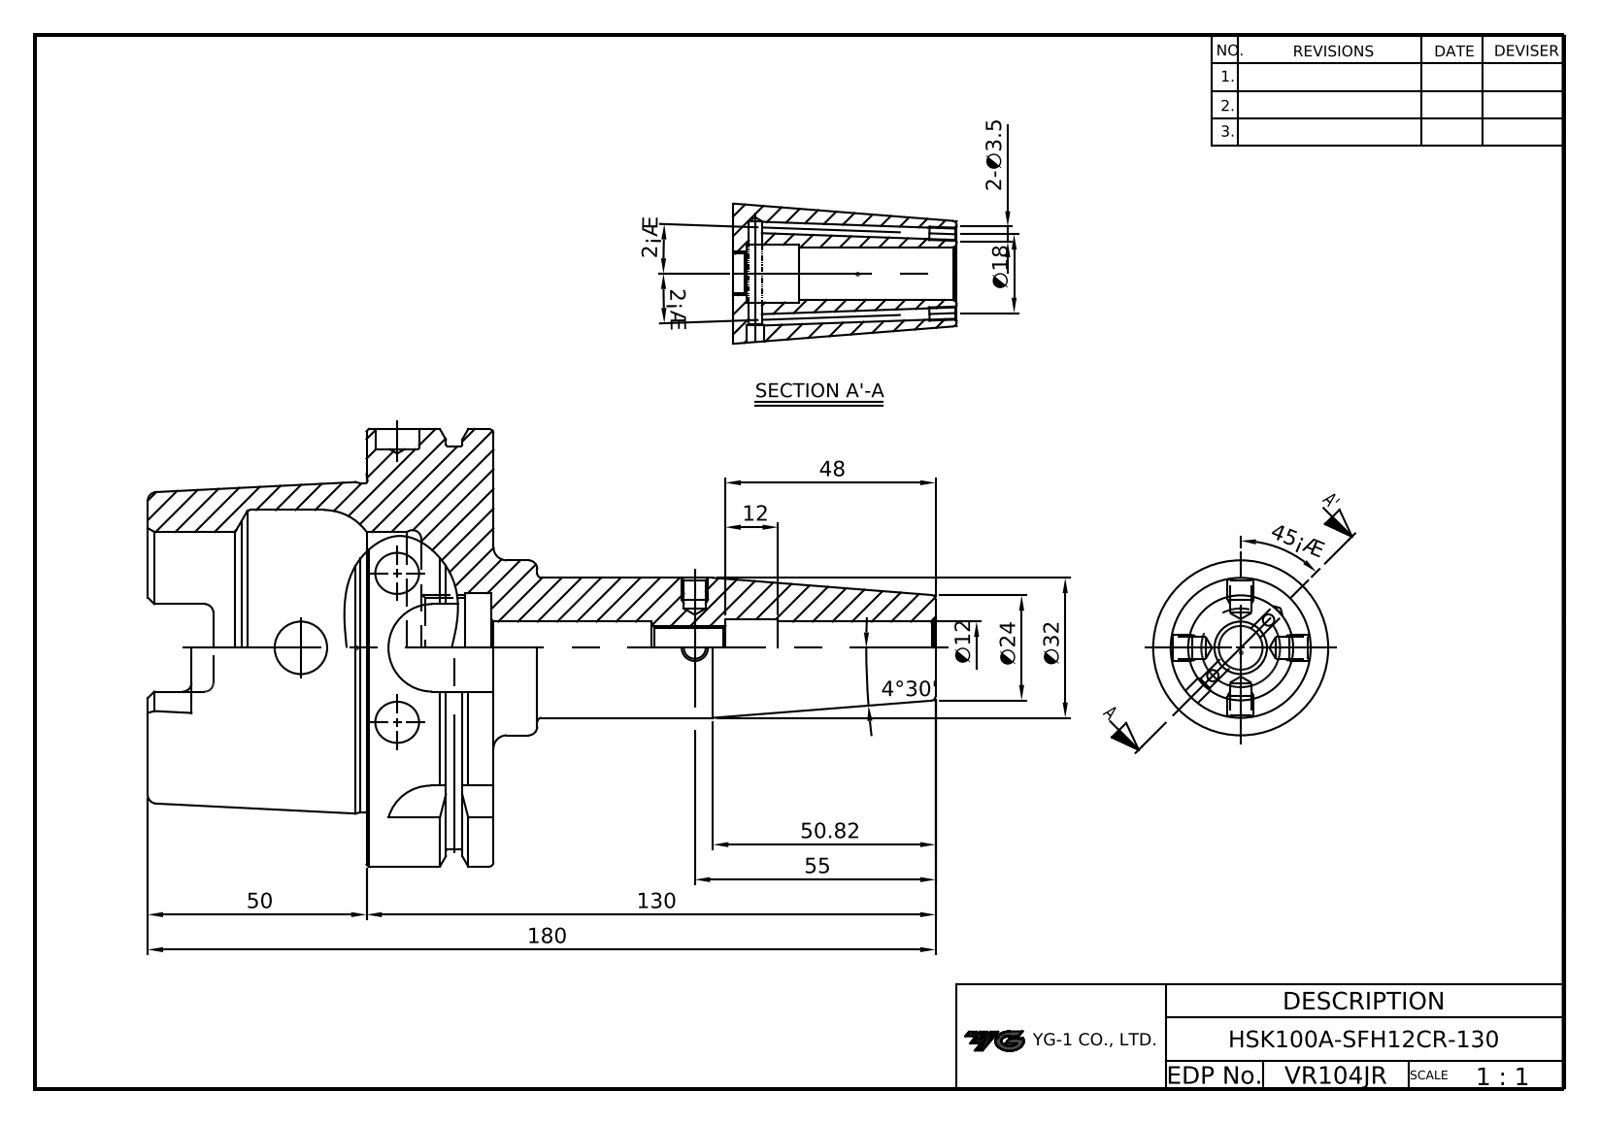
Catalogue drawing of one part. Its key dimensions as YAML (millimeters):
part_name: "LO-HSK100A-SFH12CR-130"
step_written_by: "Autodesk Inventor 2024 (AUTOMOTIVE_DESIGN)"
units: millimeters
bodies: {solids: 1, faces: 124, planar: 39, cylindrical: 38, other: 47}
overall_size: [180, 100, 100]
volume: 319434
surface_area: 63128
round_holes:
  - {diameter: 2.46, count: 2}
  - {diameter: 12, count: 2}
  - {diameter: 8.92, count: 1}
  - {diameter: 10, count: 1}
  - {diameter: 13.2, count: 1}
  - {diameter: 22.38, count: 1}
  - {diameter: 25, count: 1}
  - {diameter: 53, count: 1}
  - {diameter: 63, count: 1}
round_bosses_or_shafts:
  - {diameter: 100, count: 1}
  - {diameter: 92, count: 1}
  - {diameter: 75.41, count: 1}
  - {diameter: 40, count: 1}
  - {diameter: 32, count: 1}
partial_cylinders:
  - {radius: 2, count: 6}
  - {radius: 4.88, count: 4}
  - {radius: 10, count: 4}
face_to_face_distances: [29, 12.5, 16.5, 79, 62.5, 50, 10, 88, 78.5, 28.5]
